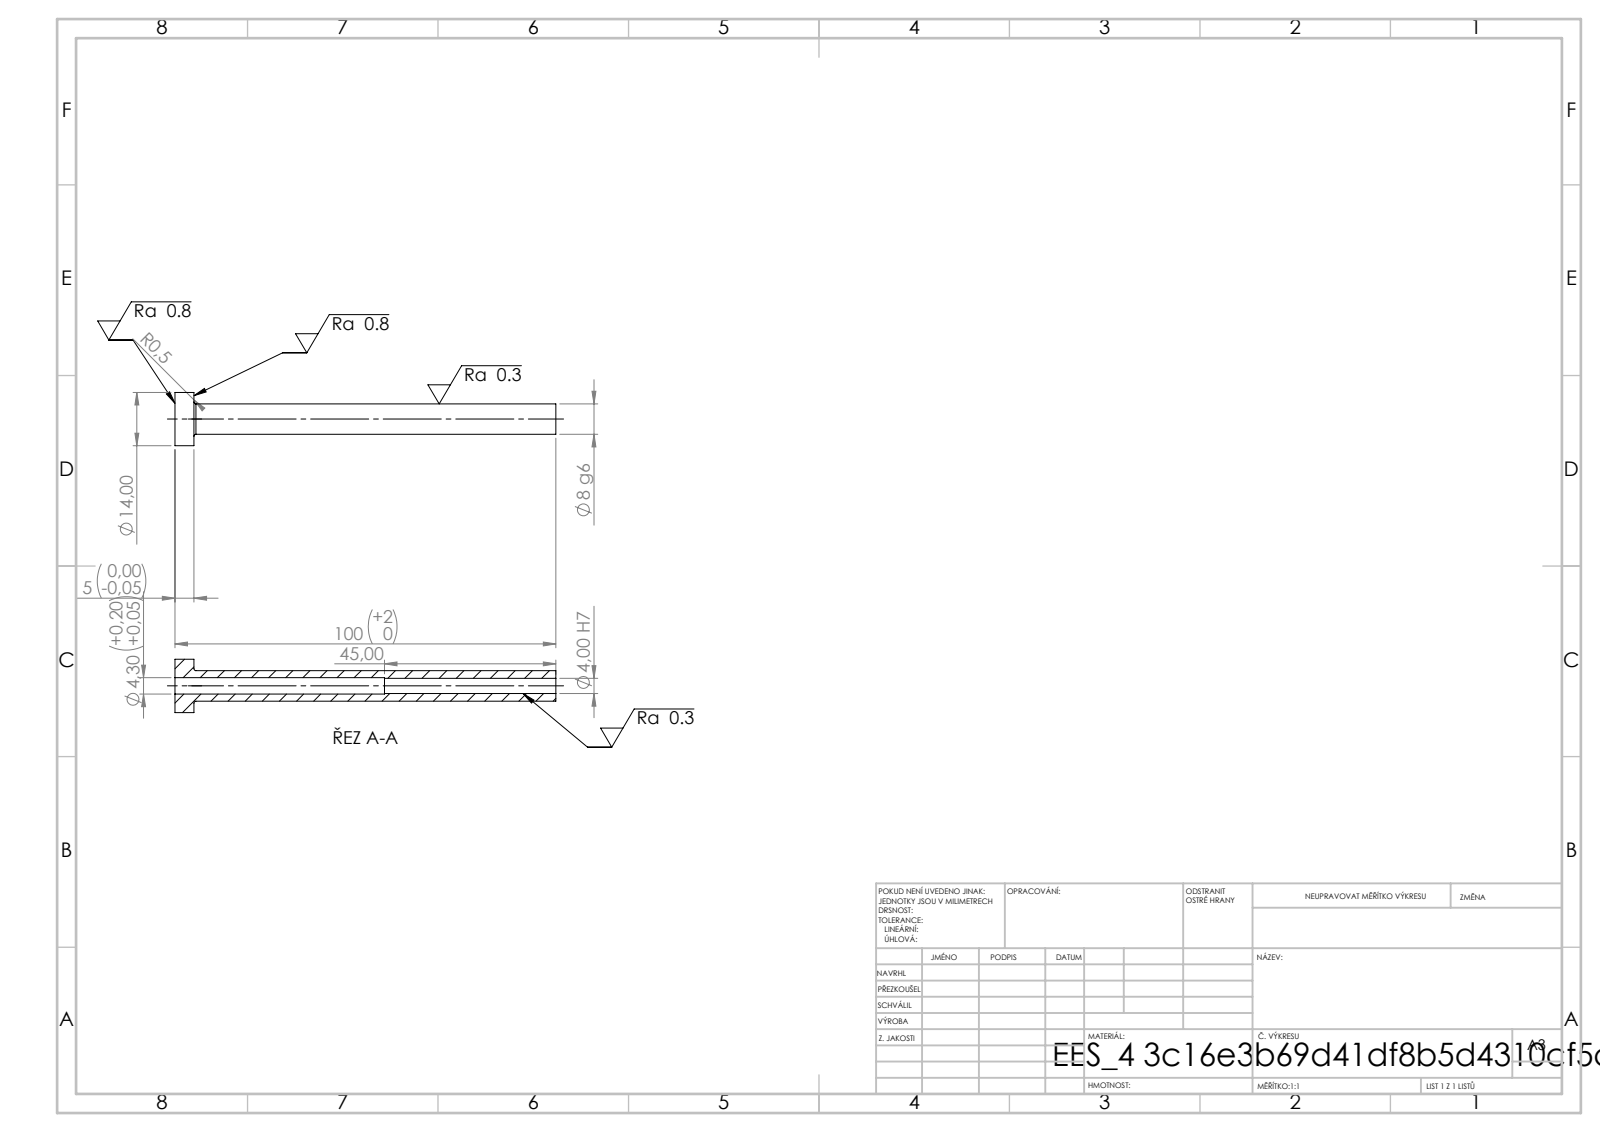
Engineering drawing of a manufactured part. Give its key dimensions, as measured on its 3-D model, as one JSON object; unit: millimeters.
{"step_written_by": "SolidWorks 2019 (CONFIG_CONTROL_DESIGN)", "units": "millimeters", "bodies": {"solids": 1, "faces": 14, "planar": 4, "cylindrical": 8, "other": 2}, "overall_size": [100, 14, 14], "volume_mm3": 4182, "surface_area_mm2": 4193, "round_holes": [[4, 1], [4.3, 1]], "round_bosses_or_shafts": [[14, 1], [8, 1]], "face_to_face_distances": [5, 100, 95, 55, 50, 45]}
